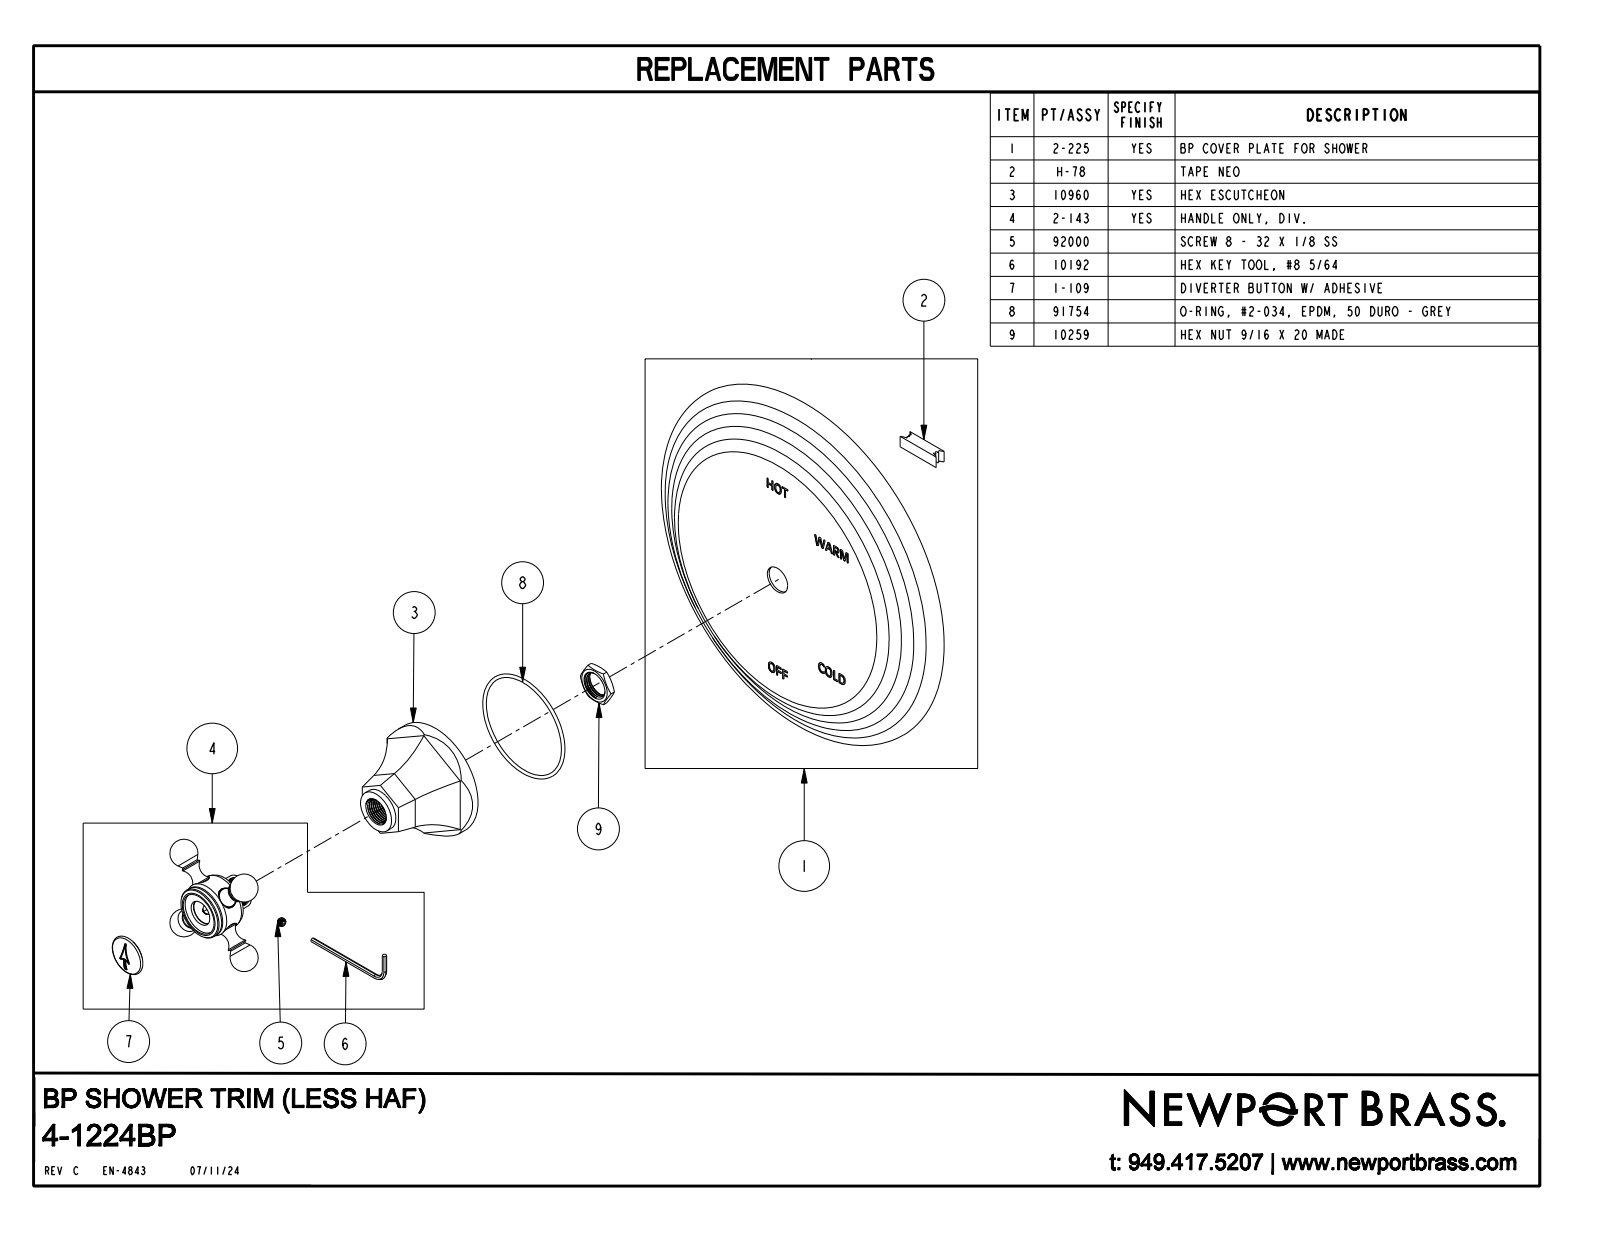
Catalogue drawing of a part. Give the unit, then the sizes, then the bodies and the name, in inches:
Units: inches
Overall size (bounding box): 7.75 × 7.75 × 3.616
Round holes (diameter × count): ⌀0.41 ×2, ⌀0.855 ×1
Round bosses / shafts (diameter × count): ⌀0.392 ×2, ⌀2.375 ×1, ⌀1.055 ×1, ⌀0.86 ×1, ⌀0.687 ×1, ⌀0.4 ×1
Partial cylindrical surfaces — rounded edges, fillets, slot ends (radius × count): R1.541 ×6, R0.015 ×2, R1 ×2, R1.02 ×2, R0.02 ×1
Main face-to-face distances: 0.754, 2.401, 1.647, 2.281, 1.527, 0.12, 0.75, 1.531, 1.651, 2.421
Volume: 32.38 in³ · Surface area: 117.6 in²
Bodies: 1 solid, 364 faces (159 planar, 41 cylindrical, 164 other)
Part name (STEP PRODUCT): 4-1224BP
STEP written by: CREO PARAMETRIC BY PTC INC, 2018400 (CONFIG_CONTROL_DESIGN)
